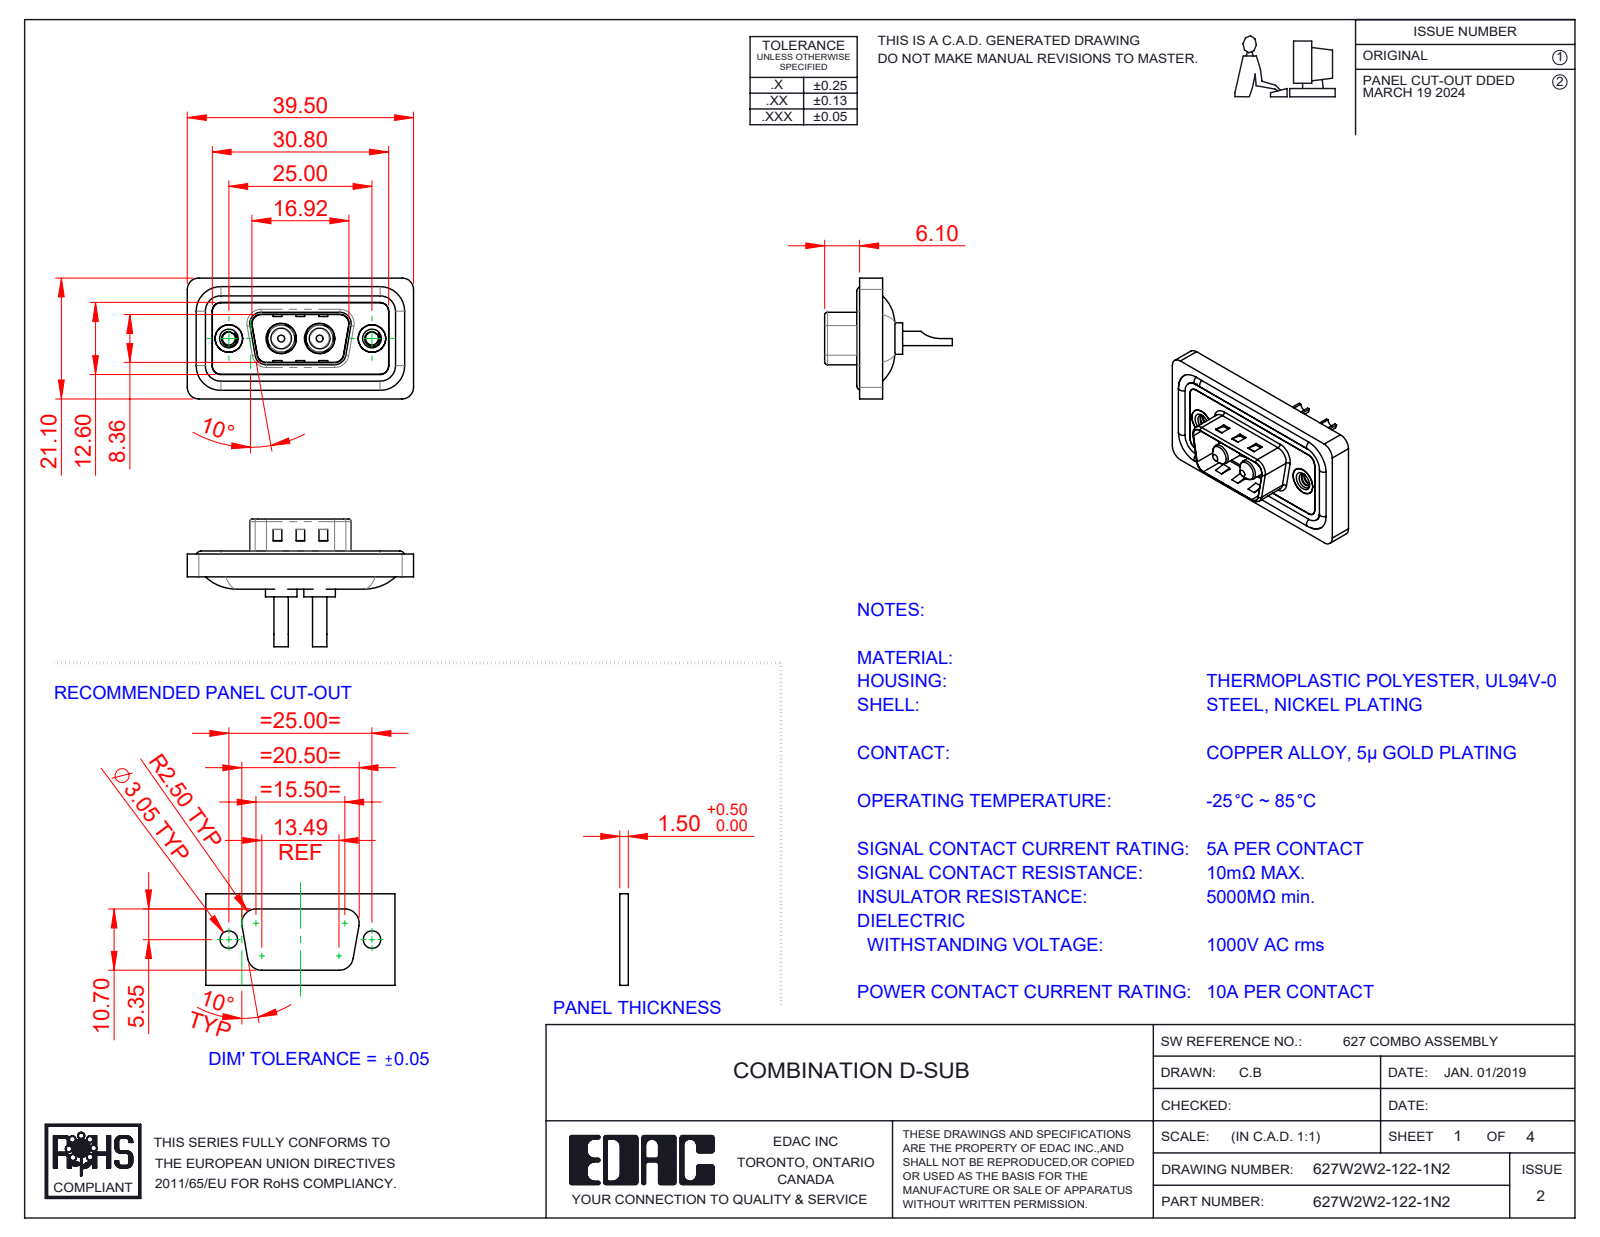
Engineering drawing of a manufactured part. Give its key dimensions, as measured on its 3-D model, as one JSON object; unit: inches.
{"part_name": "627W2W2-122-1N2; 627Combo Threaded Rivet_2; 627Combo Shell Rear_09 Contacts; 627Combo Housing_2W2 (+3 more)", "step_written_by": "SolidWorks 2023 (CONFIG_CONTROL_DESIGN)", "units": "inches", "bodies": {"solids": 11, "faces": 499, "planar": 169, "cylindrical": 224, "other": 106}, "overall_size": [1.555, 0.878, 0.831], "volume_in3": 0.272, "surface_area_in2": 10.97, "round_holes": [[0.067, 2], [0.089, 2], [0.157, 2], [0.189, 2], [0.191, 2], [0.197, 2], [0.209, 2]], "round_bosses_or_shafts": [[0.063, 4], [0.217, 2], [0.205, 2], [0.193, 2], [0.187, 2], [0.148, 2], [0.142, 2], [0.098, 2]], "partial_cylinders_radius": [[0.059, 22], [0.079, 18], [0.02, 8], [0.063, 8], [0.01, 4], [0.024, 4], [0.026, 4], [0.035, 4]], "face_to_face_distances": [0.016, 0.043, 0.114, 0.122, 0.02, 0.059, 0.063, 0.157, 0.098, 0.028], "hole_center_spacings": [0.36, 0.624, 0.265, 0.984]}
